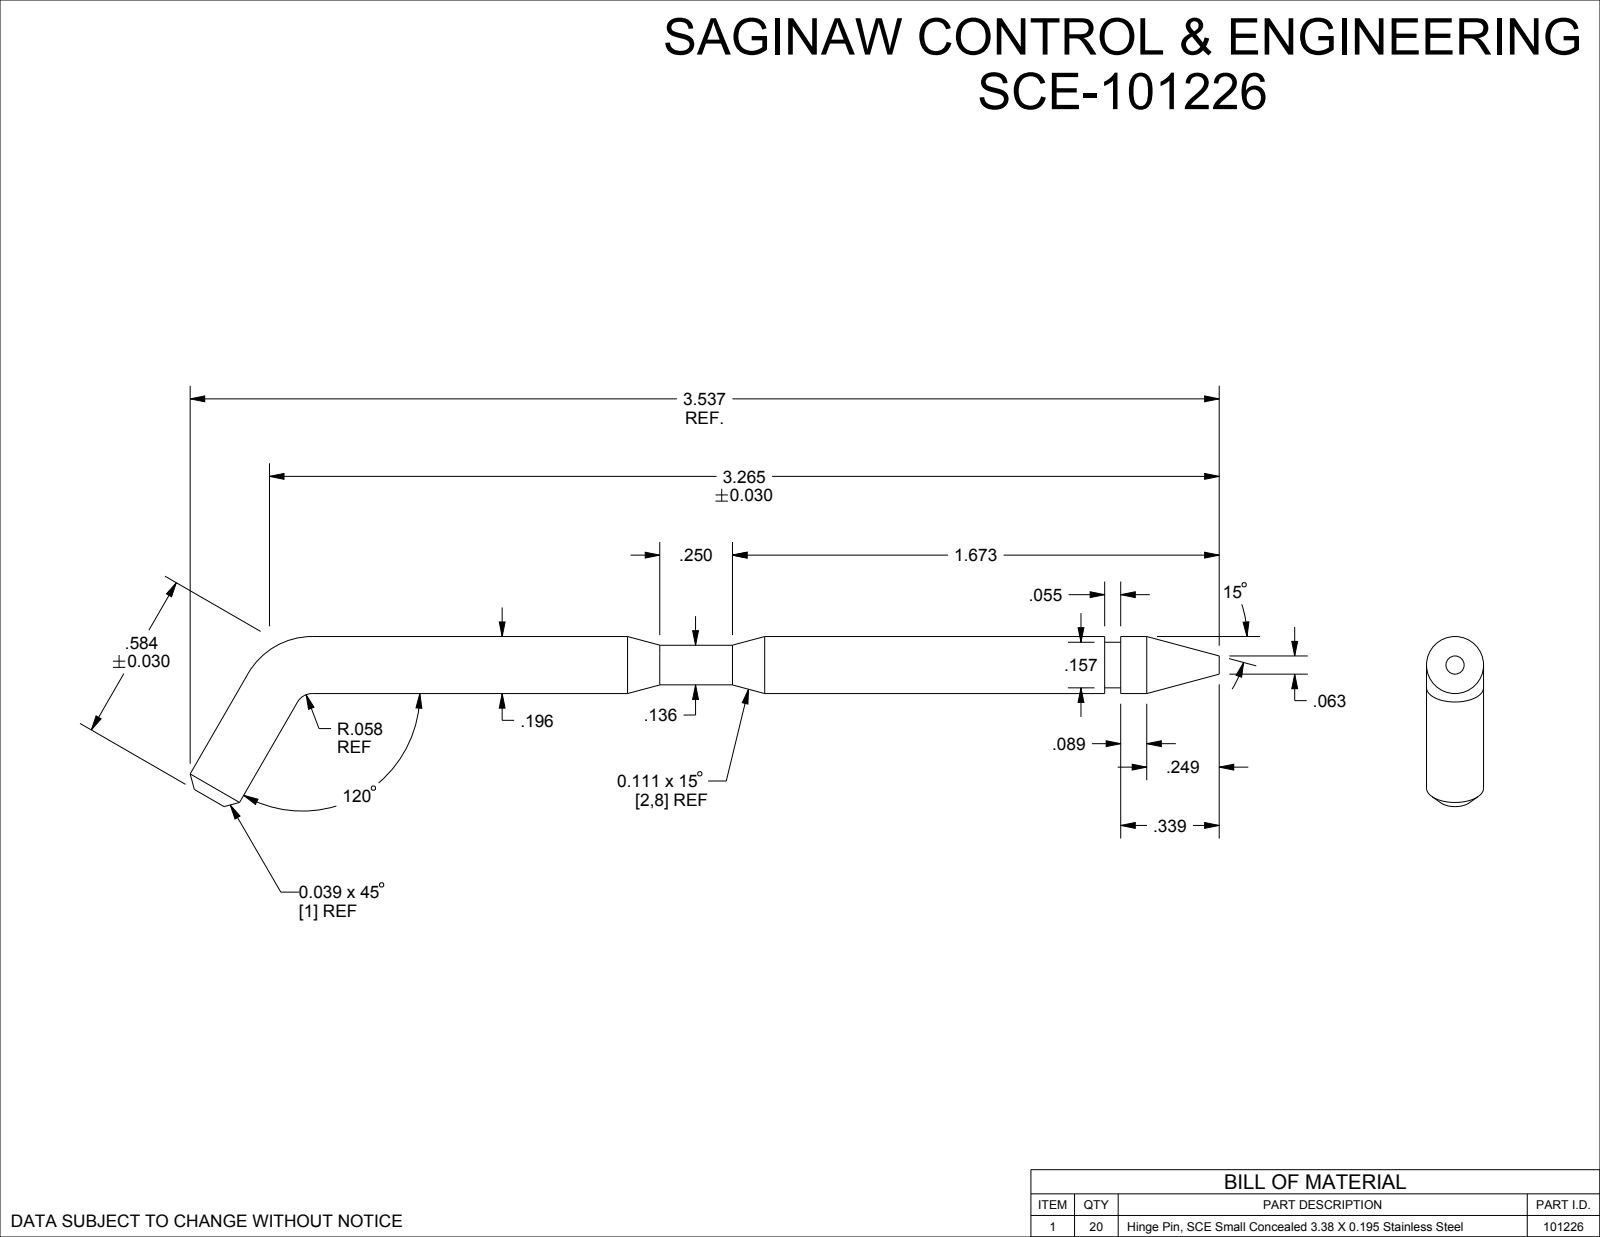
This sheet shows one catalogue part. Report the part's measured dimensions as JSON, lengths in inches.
{"part_name": "SCE-101226", "step_written_by": "SolidWorks 2019 (AUTOMOTIVE_DESIGN)", "units": "inches", "bodies": {"solids": 1, "faces": 26, "planar": 4, "cylindrical": 12, "other": 10}, "overall_size": [3.537, 0.584, 0.196], "volume_in3": 0.102, "surface_area_in2": 2.21, "round_bosses_or_shafts": [[0.196, 2], [0.157, 1], [0.136, 1]], "face_to_face_distances": [0.055, 0.339, 0.394]}
